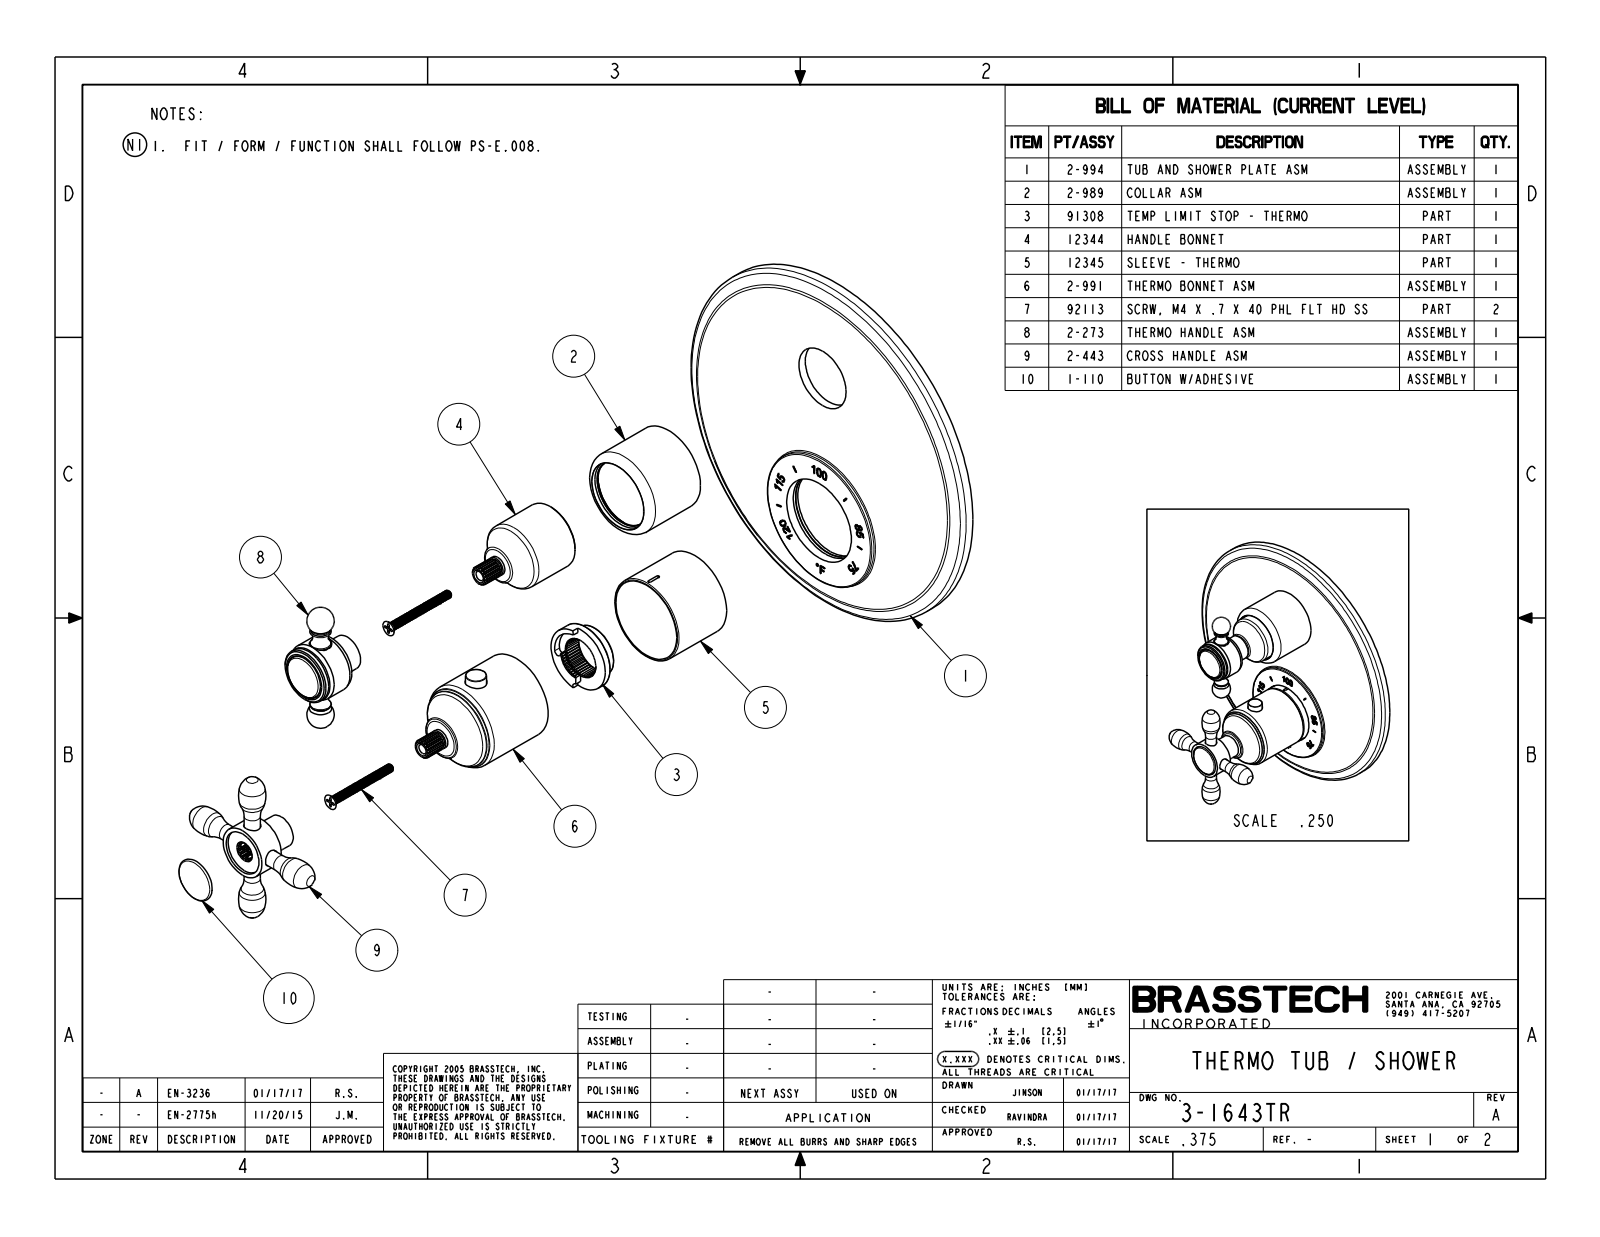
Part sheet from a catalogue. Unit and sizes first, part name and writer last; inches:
Units: inches
Overall size (bounding box): 7.087 × 7.087 × 4.375
Round holes (diameter × count): ⌀0.136 ×4, ⌀0.19 ×2, ⌀0.206 ×2, ⌀0.27 ×2, ⌀0.313 ×2, ⌀0.057 ×1, ⌀0.079 ×1, ⌀0.1 ×1, ⌀0.126 ×1, ⌀0.205 ×1, ⌀0.276 ×1, ⌀0.276 ×1
Round bosses / shafts (diameter × count): ⌀0.164 ×4, ⌀0.25 ×3, ⌀0.18 ×3, ⌀0.157 ×3, ⌀1.654 ×2, ⌀0.512 ×2, ⌀0.37 ×2, ⌀0.303 ×2
Partial cylindrical surfaces — rounded edges, fillets, slot ends (radius × count): R0.047 ×3, R0.169 ×3, R0.17 ×3, R0.039 ×2, R0.075 ×2, R0.082 ×2, R0.164 ×2, R0.169 ×2
Main face-to-face distances: 0.08, 0.083, 0.163, 0.17, 0.09, 0.253, 0.185, 0.268, 0.348, 0.438
Hole centre spacings: 1.617, 0.423, 0.554, 0.554, 1.019, 1.02, 1.021, 1.293
Volume: 10.16 in³ · Surface area: 280 in²
Bodies: 32 solids, 3173 faces (899 planar, 803 cylindrical, 1471 other)
Part name (STEP PRODUCT): 12346_AF0; H-78_2_FEET_AF0; 91678; 2-994_AF0_ASM (+8 more)
STEP written by: PRO/ENGINEER BY PARAMETRIC TECHNOLOGY CORPORATION, 2013150 (CONFIG_CONTROL_DESIGN)
